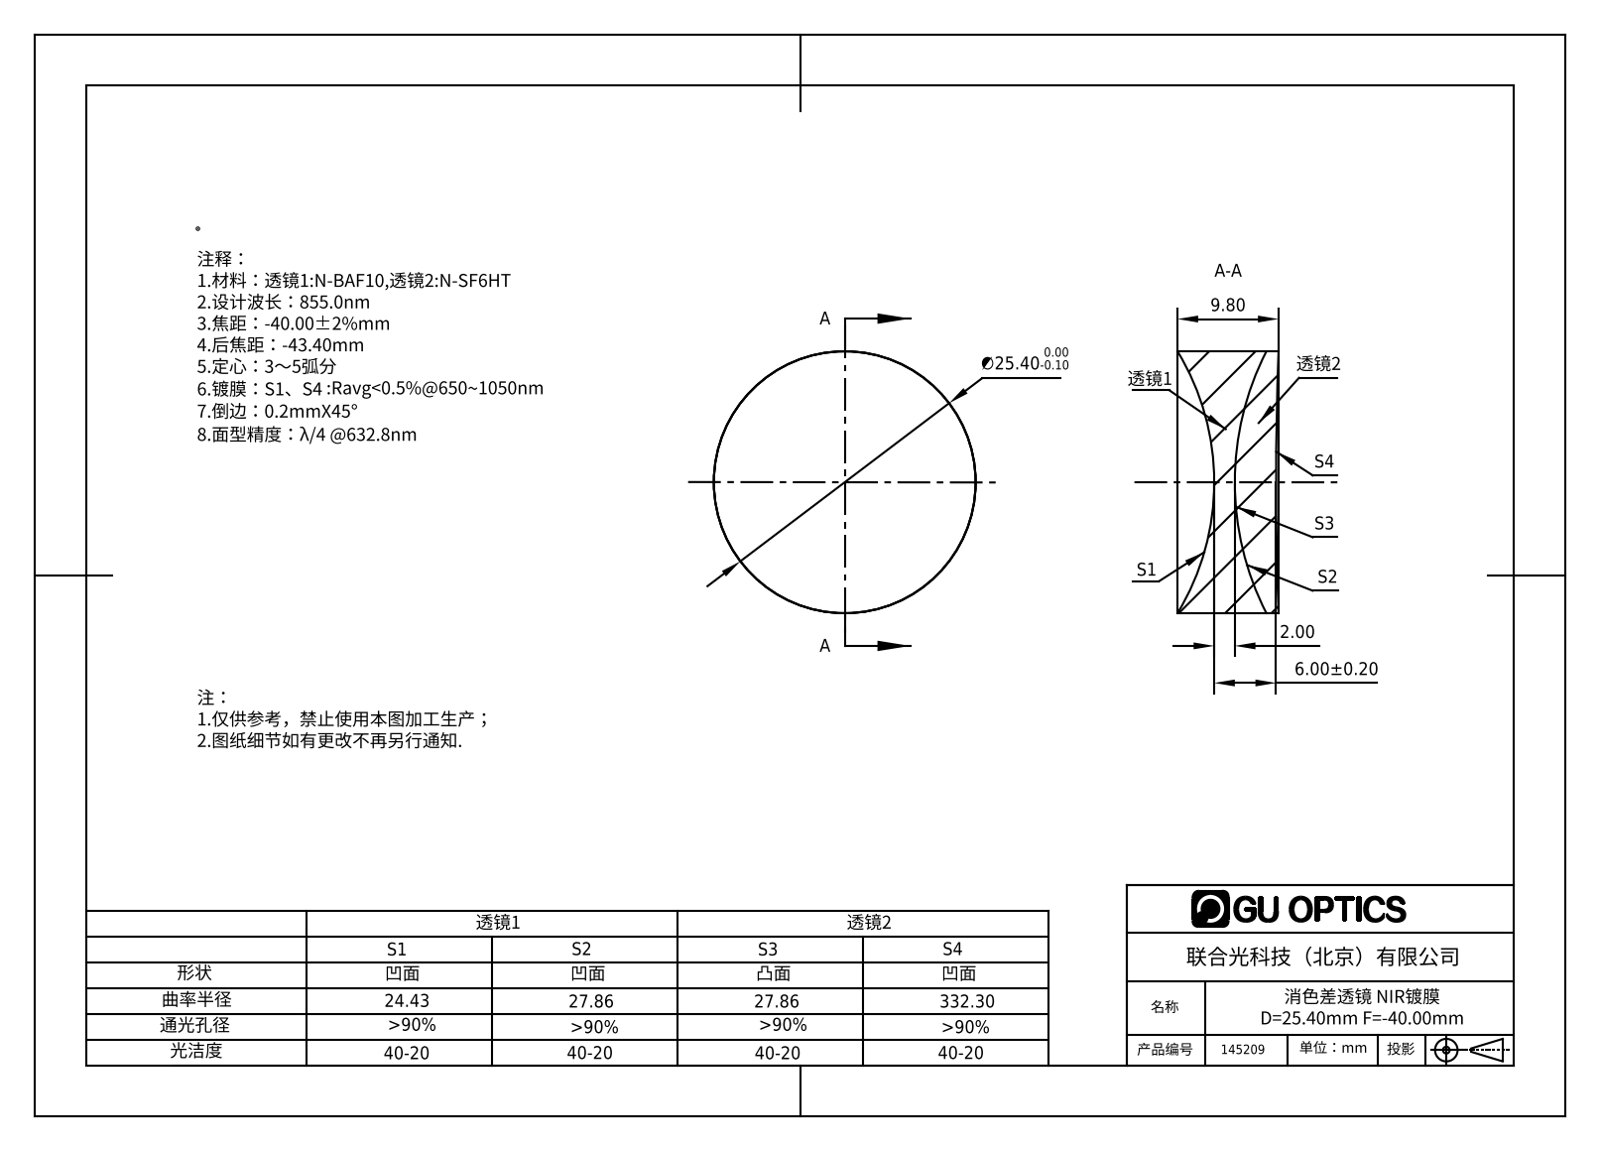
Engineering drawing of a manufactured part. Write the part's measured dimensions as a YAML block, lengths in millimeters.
part_name: "145209"
step_written_by: "SolidWorks 2016 (AUTOMOTIVE_DESIGN)"
units: millimeters
bodies: {solids: 2, faces: 12, planar: 0, cylindrical: 4, other: 8}
overall_size: [25.4, 25.4, 9.8]
volume: 3980
surface_area: 2908
round_bosses_or_shafts:
  - {diameter: 25.4, count: 1}
